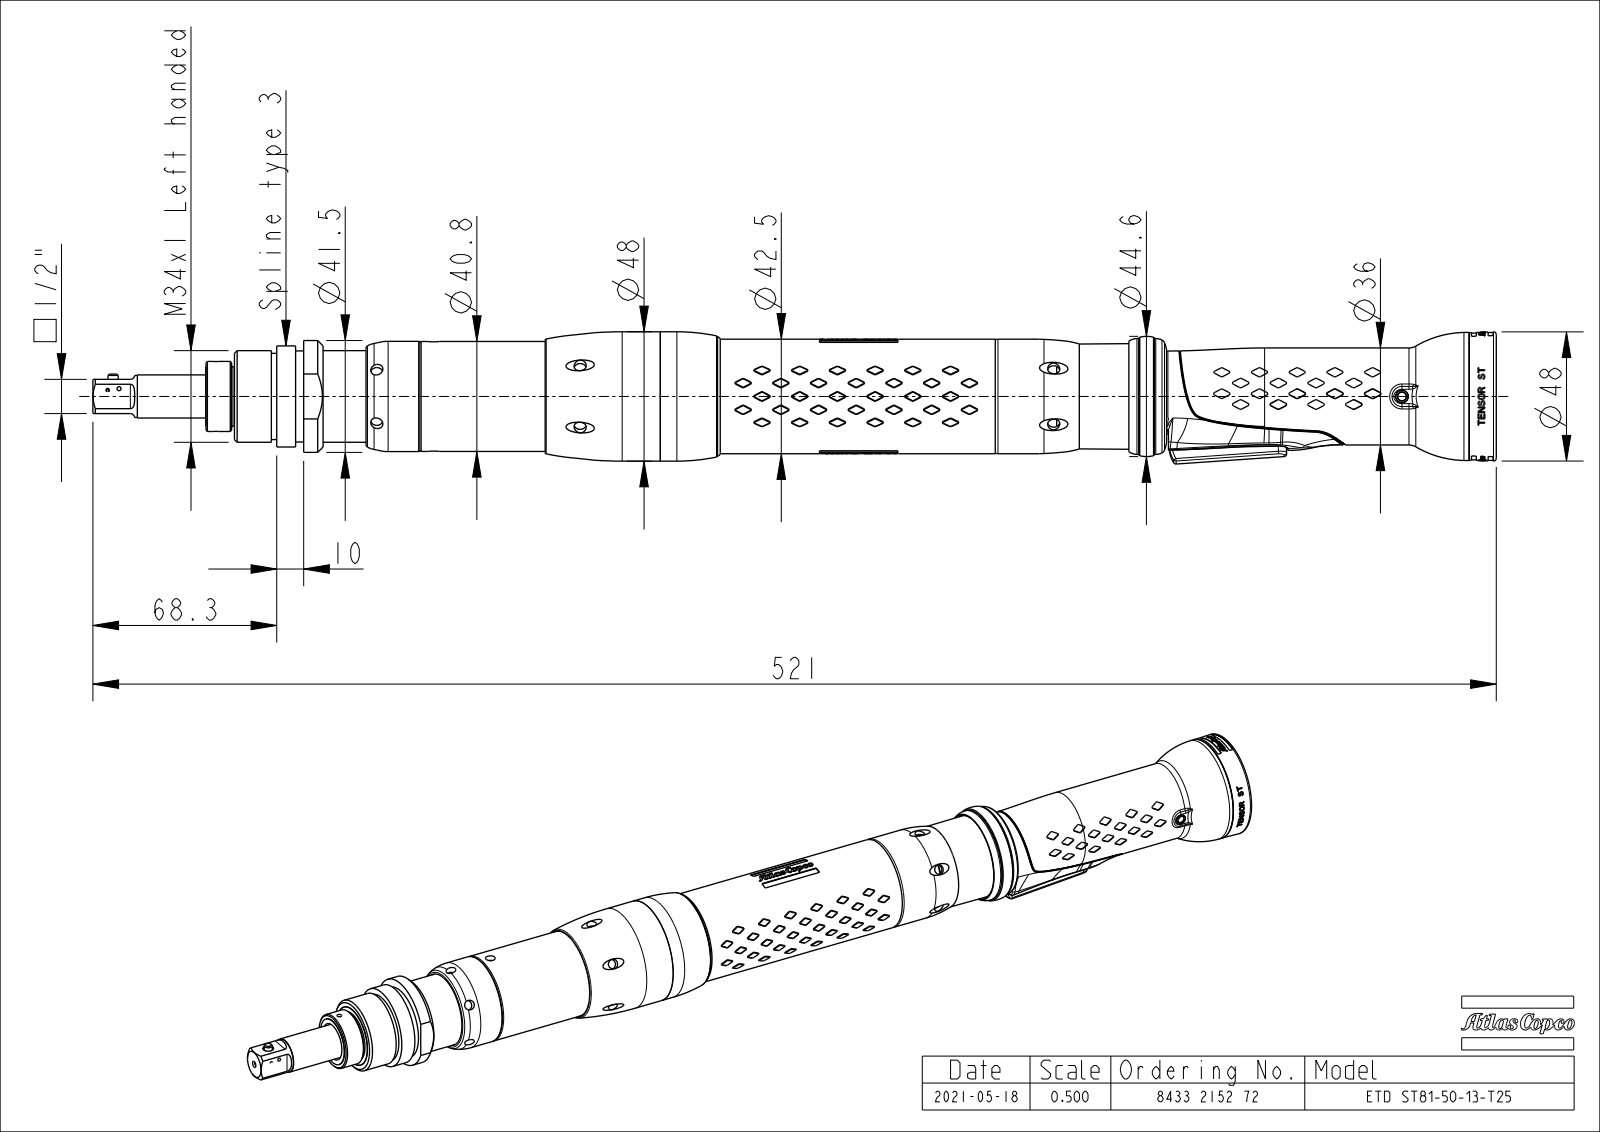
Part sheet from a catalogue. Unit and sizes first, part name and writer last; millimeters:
Units: millimetres
Overall size (bounding box): 521.01 × 49.07 × 48
Round holes (diameter × count): ⌀4.5 ×10, ⌀2 ×3, ⌀2.2 ×2, ⌀1.5 ×1, ⌀4.6 ×1, ⌀4.7 ×1, ⌀16.5 ×1, ⌀17.5 ×1, ⌀18.6 ×1, ⌀23 ×1, ⌀29.7 ×1, ⌀36.4 ×1
Round bosses / shafts (diameter × count): ⌀48 ×1, ⌀46 ×1, ⌀45 ×1, ⌀44.41 ×1, ⌀43.9 ×1, ⌀43 ×1, ⌀42.99 ×1, ⌀42.9 ×1
Partial cylindrical surfaces — rounded edges, fillets, slot ends (radius × count): R0.5 ×11, R1 ×11, R0.3 ×8, R2 ×8, R3 ×8, R1.5 ×6, R0.2 ×4, R0.7 ×4
Main face-to-face distances: 2.1, 106, 21.5, 158.6, 22, 136.6, 132.8, 154.8, 291.4, 19
Hole centre spacings: 75.5, 175.8, 251.3, 3.4, 21.1, 24.5, 27.4, 29
Volume: 737 010 mm³ · Surface area: 204 470 mm²
Bodies: 18 solids, 3030 faces (947 planar, 462 cylindrical, 1621 other)
Part name (STEP PRODUCT): 4220232200; 4220232310; 4220249500_SPEC; 4220232380_ASM (+8 more)
STEP written by: CREO PARAMETRIC BY PTC INC, 2020454 (CONFIG_CONTROL_DESIGN)
